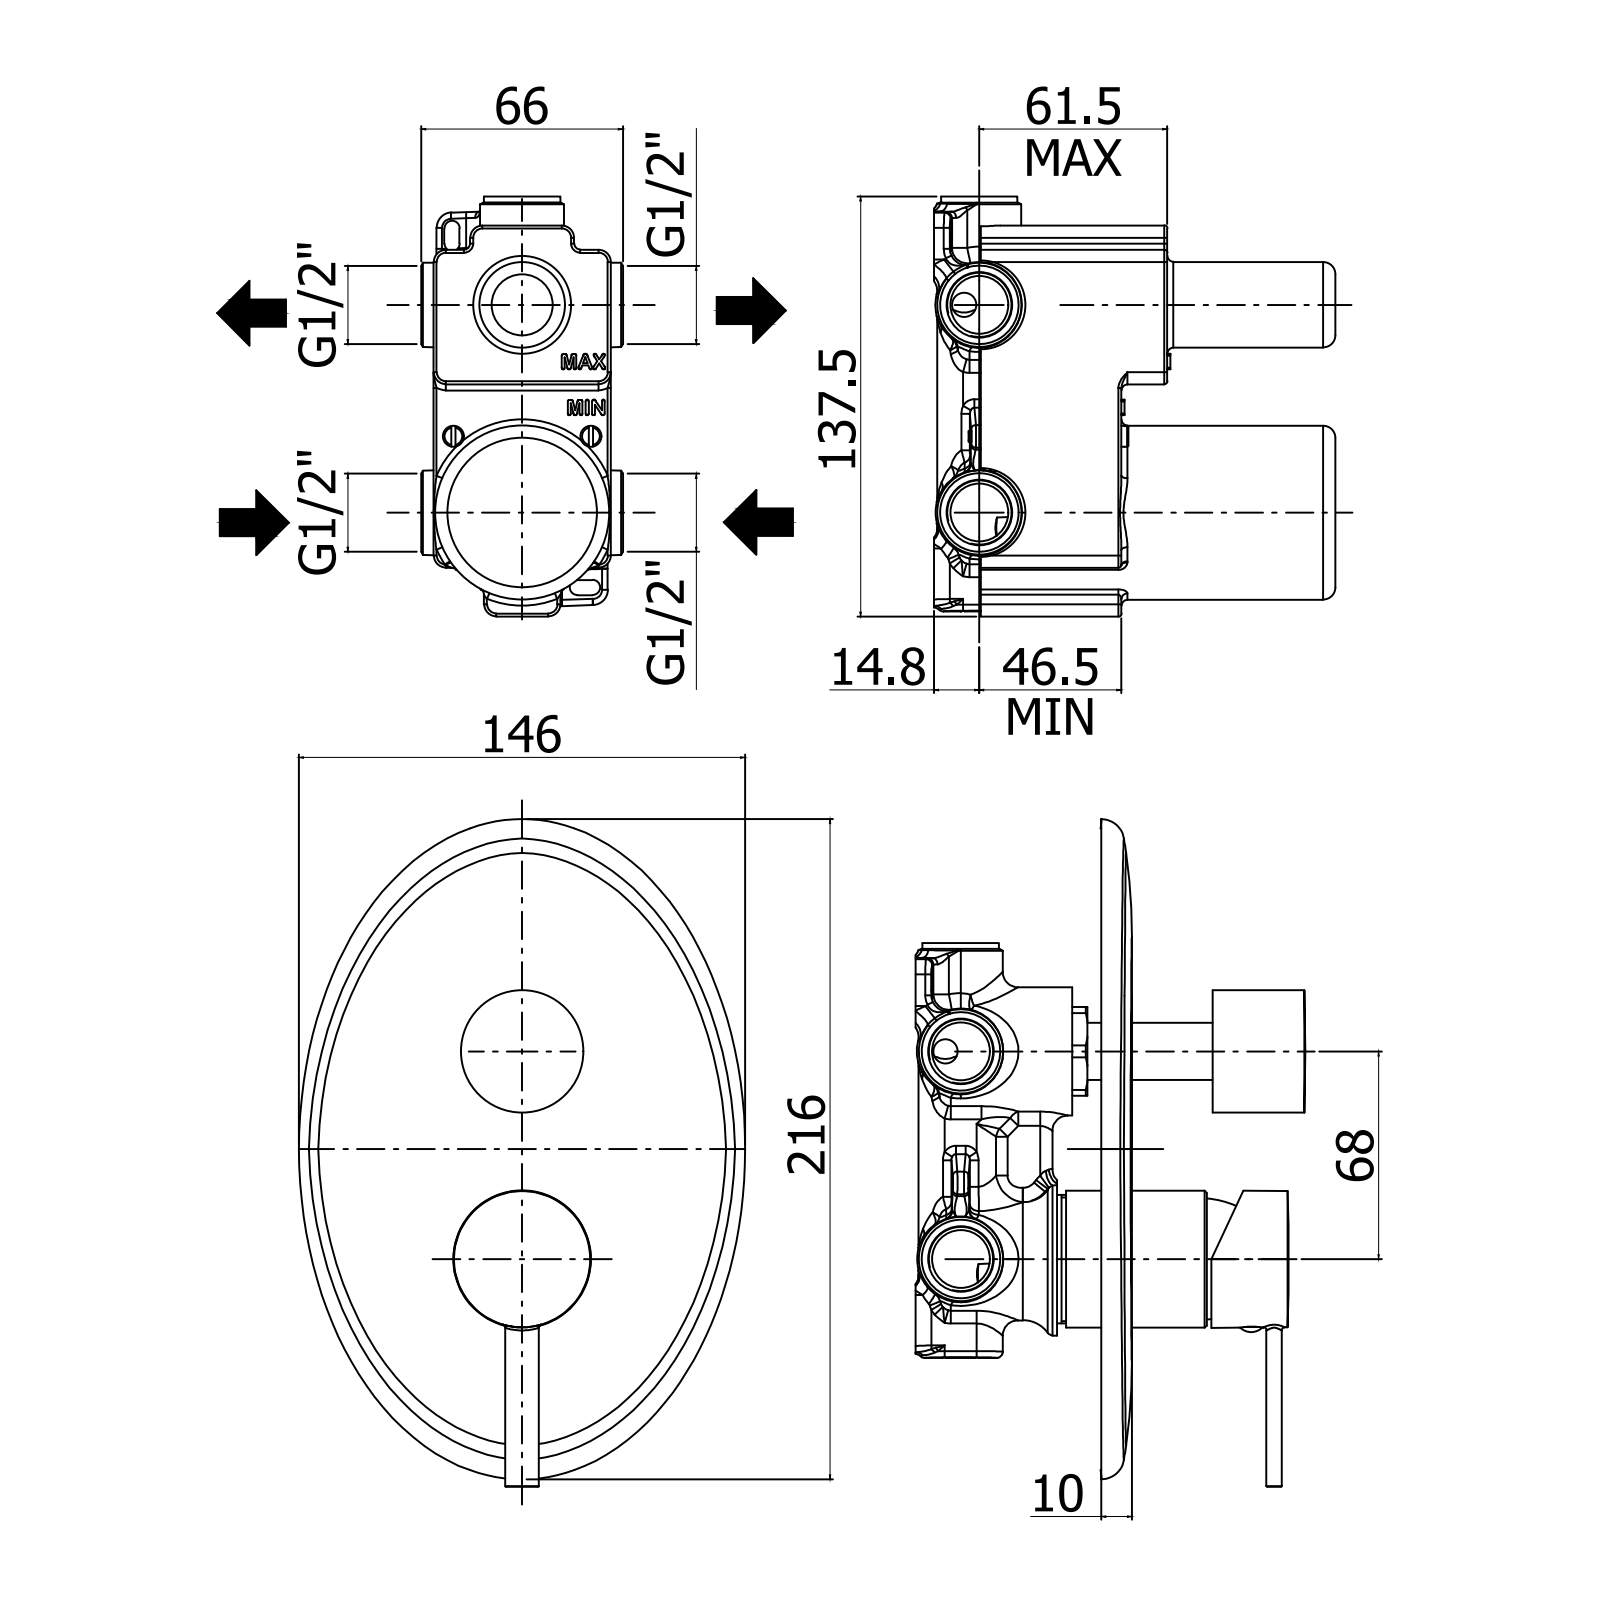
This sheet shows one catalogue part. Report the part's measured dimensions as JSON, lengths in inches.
{"part_name": "BR018CR", "step_written_by": "CREO PARAMETRIC BY PTC INC, 2020044 (CONFIG_CONTROL_DESIGN)", "units": "inches", "bodies": {"solids": 4, "faces": 1287, "planar": 718, "cylindrical": 312, "other": 257}, "overall_size": [8.504, 5.748, 2.49], "volume_in3": 8.674, "surface_area_in2": 167.2, "round_holes": [[0.118, 2], [0.157, 2], [0.5, 2], [1.417, 2], [0.126, 1], [0.13, 1], [0.138, 1], [0.165, 1], [0.177, 1], [0.197, 1], [0.315, 1], [0.433, 1]], "round_bosses_or_shafts": [[0.366, 2], [2.008, 1], [1.929, 1], [1.764, 1], [1.575, 1], [1.378, 1], [1.37, 1], [1.268, 1]], "partial_cylinders_radius": [[0.02, 27], [0.006, 11], [0.012, 8], [0.039, 4], [0.049, 4], [0.031, 2], [0.108, 2], [0.098, 1]], "face_to_face_distances": [2.146, 0.354, 0.15, 0.299, 1.996, 0.965, 1.181, 0.071, 1.343, 1.846], "hole_center_spacings": [0.339, 2.887, 3.279, 0.272, 0.311, 0.394, 0.551, 0.583]}
